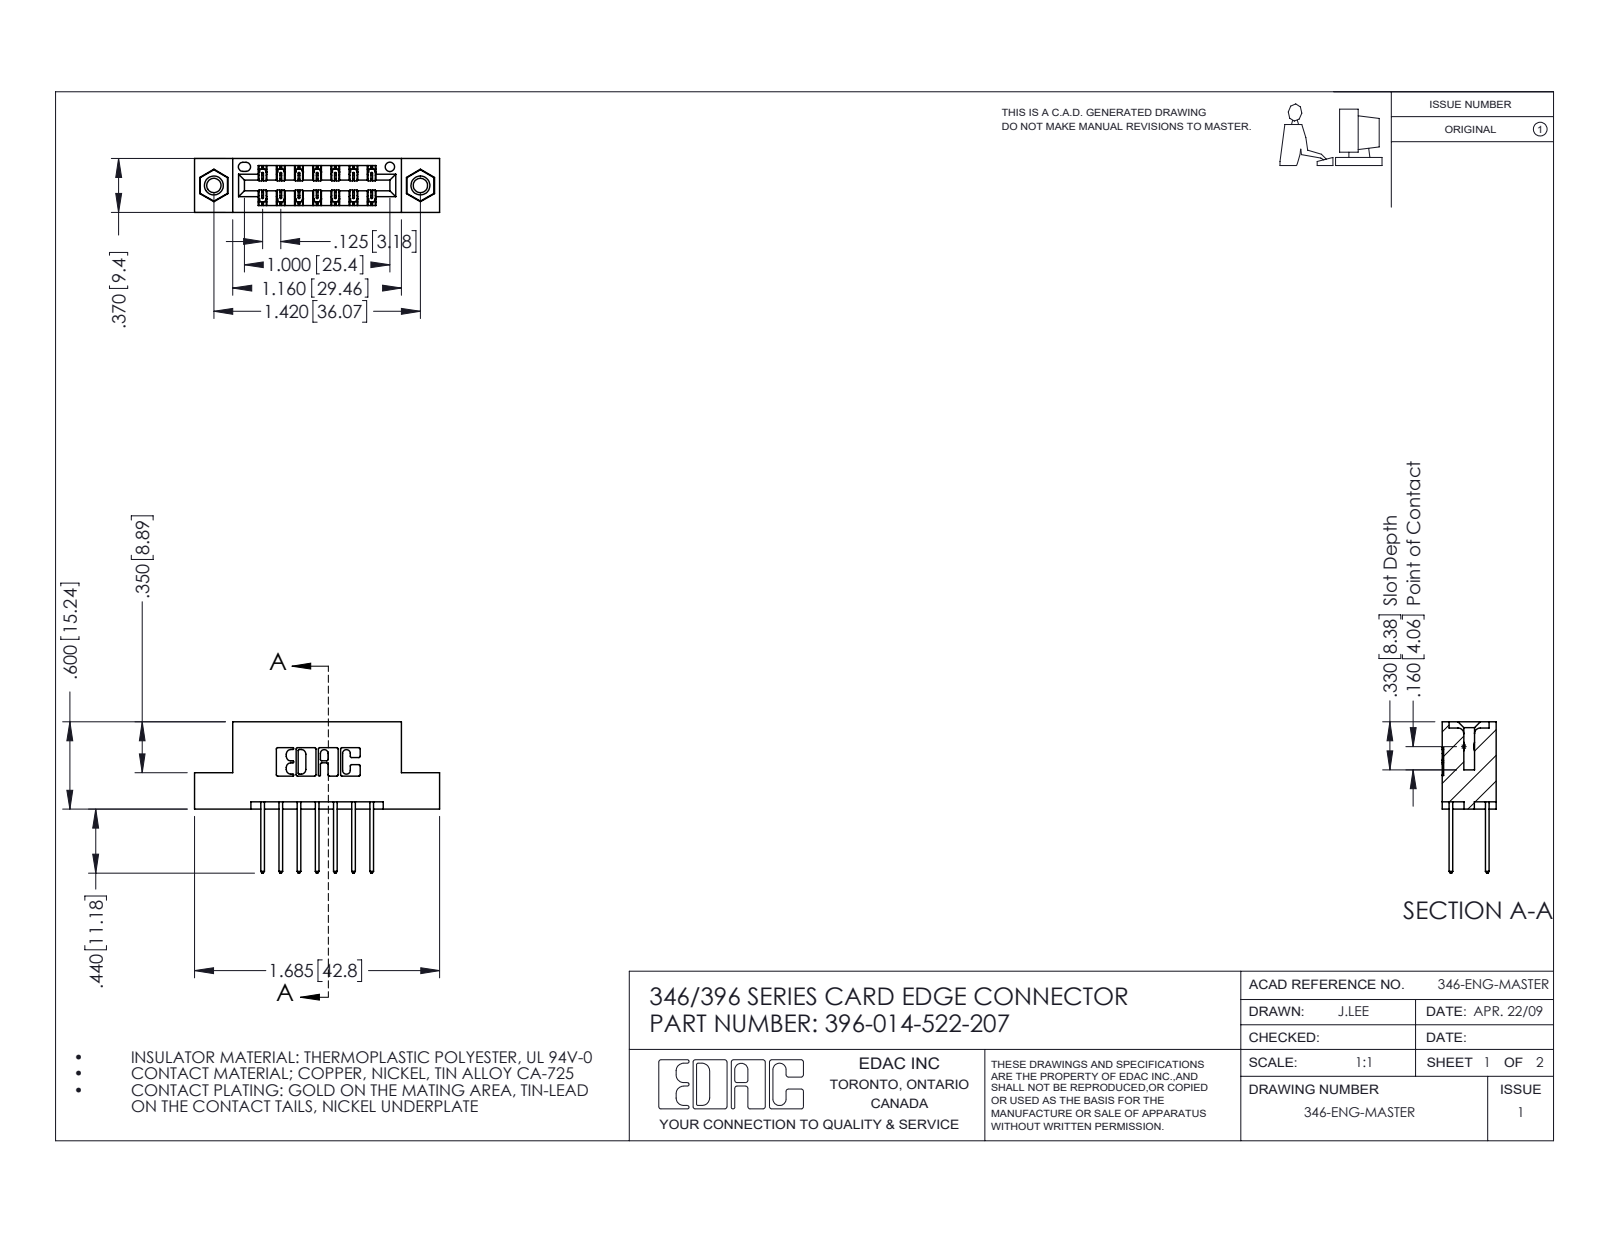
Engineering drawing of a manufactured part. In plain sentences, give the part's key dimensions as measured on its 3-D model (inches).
The part is named "345-292-001_345-293-122; 396-014-522-207; 346 Part_Flush Mounting Lugs - 0.156 Dia-TI; 345-250-001_345-250-005-103". Its 3-D file was written by "SolidWorks 2016 (CONFIG_CONTROL_DESIGN)". It is 17 solids with 910 faces: 598 planar, 296 cylindrical and 16 other. Overall it measures 1.685 by 1.04 by 0.37 inches. Its volume is 0.239 cubic inches and its surface area 7.818 square inches. Round holes: 2 of diameter 0.098, 2 of diameter 0.125, 2 of diameter 0.156, 1 of diameter 0.064. Round bosses or shafts: 2 of diameter 0.155. Partial cylindrical surfaces (rounded edges, fillets, slot ends): 22 of radius 0.01, 21 of radius 0.006, 14 of radius 0.01, 6 of radius 0.007, 6 of radius 0.031, 3 of radius 0.026, 2 of radius 0.014, 2 of radius 0.022. The main face-to-face distances are 0.25, 0.048, 0.322, 0.37, 0.025, 0.072, 0.298, 0.275, 0.148, 0.222. The hole center spacings are 0.246, 1.217, 1.42.
